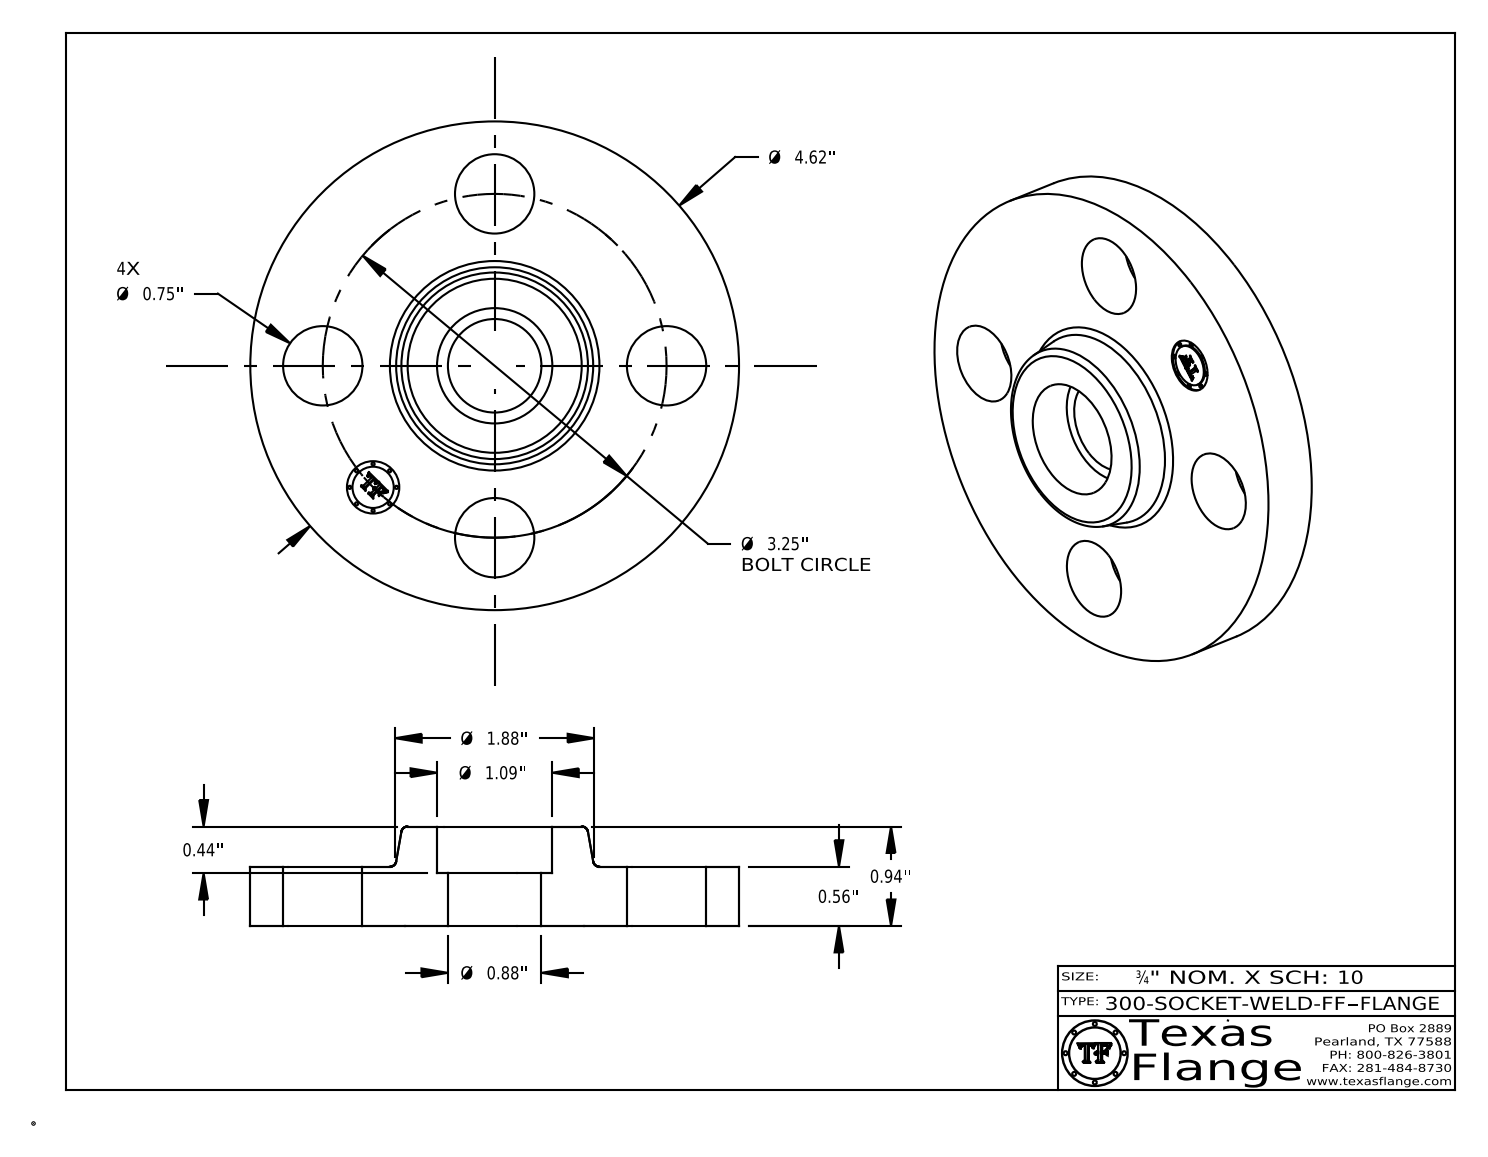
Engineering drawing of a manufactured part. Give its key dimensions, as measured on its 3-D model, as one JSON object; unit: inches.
{"part_name": "300-SOCKET-WELD-FF", "step_written_by": "CATIA V5 STEP AP214 (AUTOMOTIVE_DESIGN)", "units": "inches", "bodies": {"solids": 1, "faces": 410, "planar": 370, "cylindrical": 34, "other": 6}, "overall_size": [4.62, 4.62, 0.94], "volume_in3": 8.661, "surface_area_in2": 46.78, "round_holes": [[0.75, 4], [0.495, 1], [0.884, 1], [1.09, 1]], "round_bosses_or_shafts": [[0.03, 8], [4.62, 1], [0.39, 1]], "face_to_face_distances": [0.56, 0.94, 0.38, 0.5, 0.06, 0.44, 0.545, 0.045, 0.015, 0.395], "hole_center_spacings": [1.625, 2.298, 1.244, 3.003, 3.25]}
